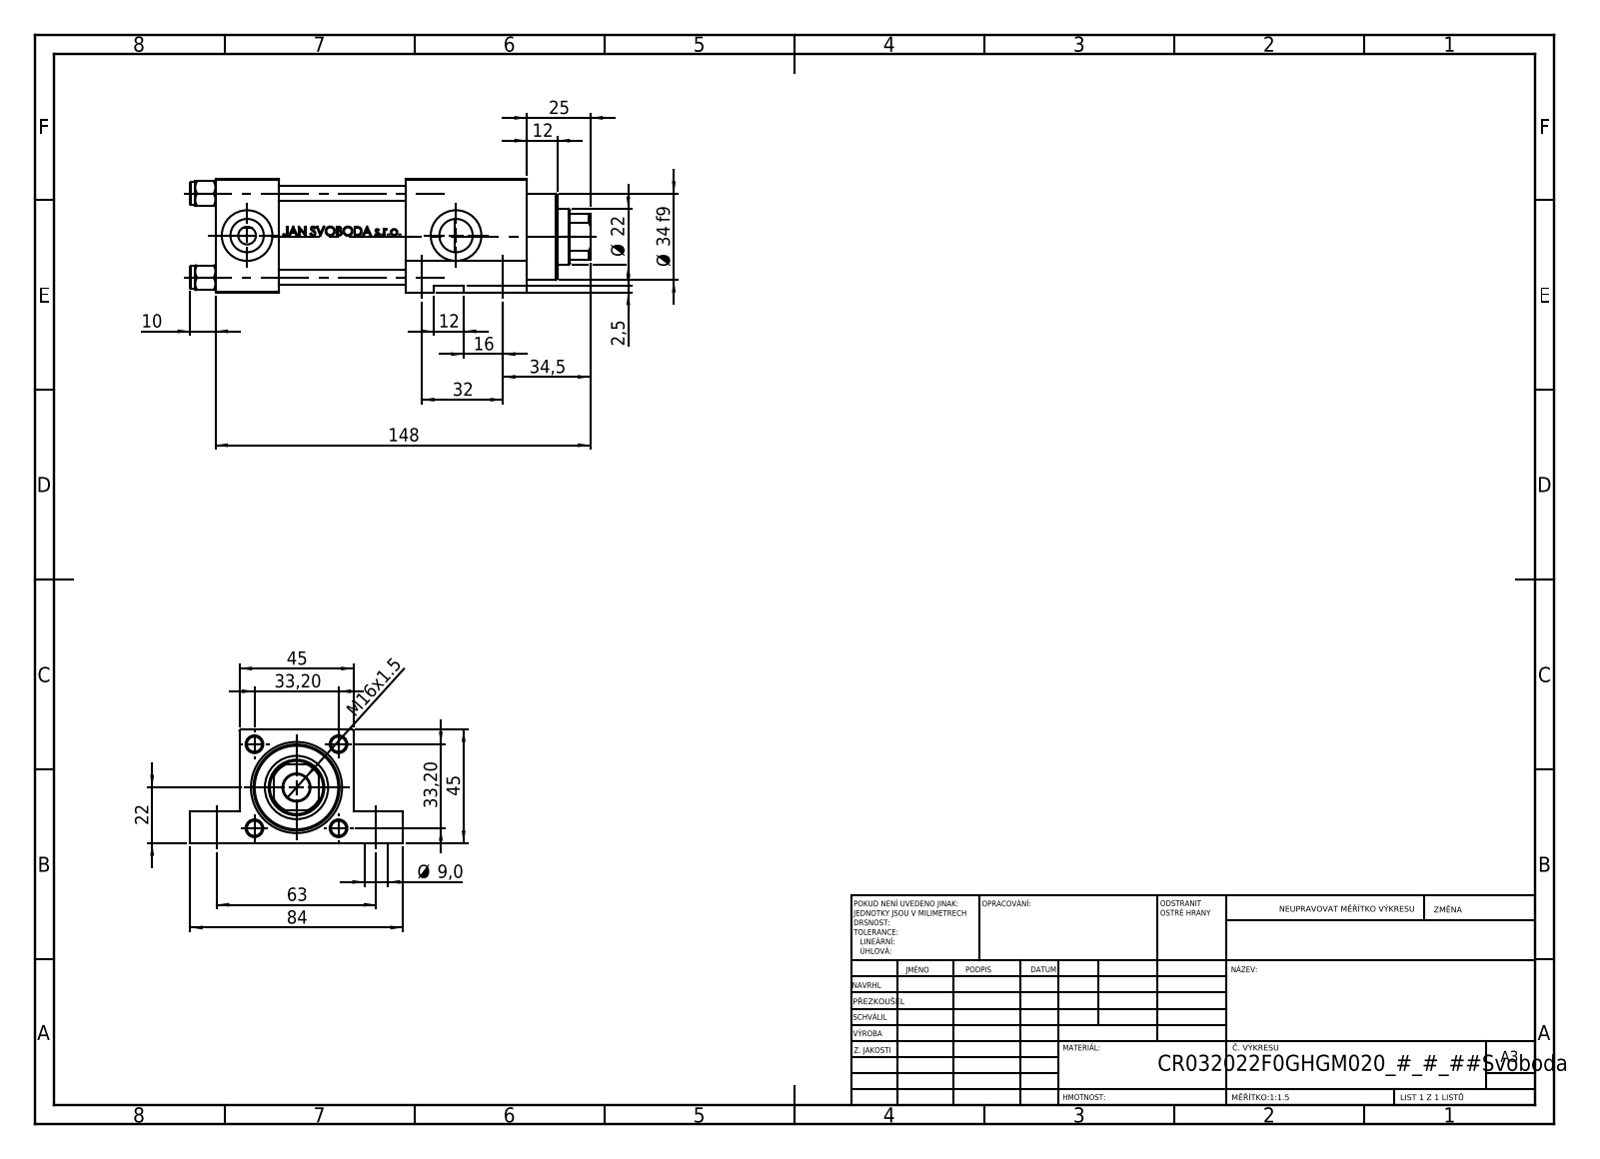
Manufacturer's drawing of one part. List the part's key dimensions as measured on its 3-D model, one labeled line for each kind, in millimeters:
Part name (STEP PRODUCT): NUT_M5_F; V215_VC_A; V215CR_VCP_F; V215CR_F_TYCINKA (+1 more)
STEP written by: SolidWorks 2019 (CONFIG_CONTROL_DESIGN)
Units: millimetres
Bodies: 11 solids, 1102 faces (436 planar, 126 cylindrical, 540 other)
Overall size (bounding box): 158 × 84 × 45
Volume: 228 209 mm³ · Surface area: 76 802 mm²
Round holes (diameter × count): ⌀6 ×4, ⌀9 ×4, ⌀7 ×2, ⌀13.16 ×2, ⌀20 ×2, ⌀10.5 ×1, ⌀22 ×1, ⌀24 ×1, ⌀25 ×1, ⌀32 ×1, ⌀33 ×1
Round bosses / shafts (diameter × count): ⌀9 ×4, ⌀38 ×1, ⌀34 ×1
Partial cylindrical surfaces — rounded edges, fillets, slot ends (radius × count): R10.5 ×1
Main face-to-face distances: 45, 25, 50, 98, 123, 75, 12.5, 32.5, 48, 10
Hole centre spacings: 33.2, 23.13, 23.83, 32, 46.95, 63, 70.66, 82.5
